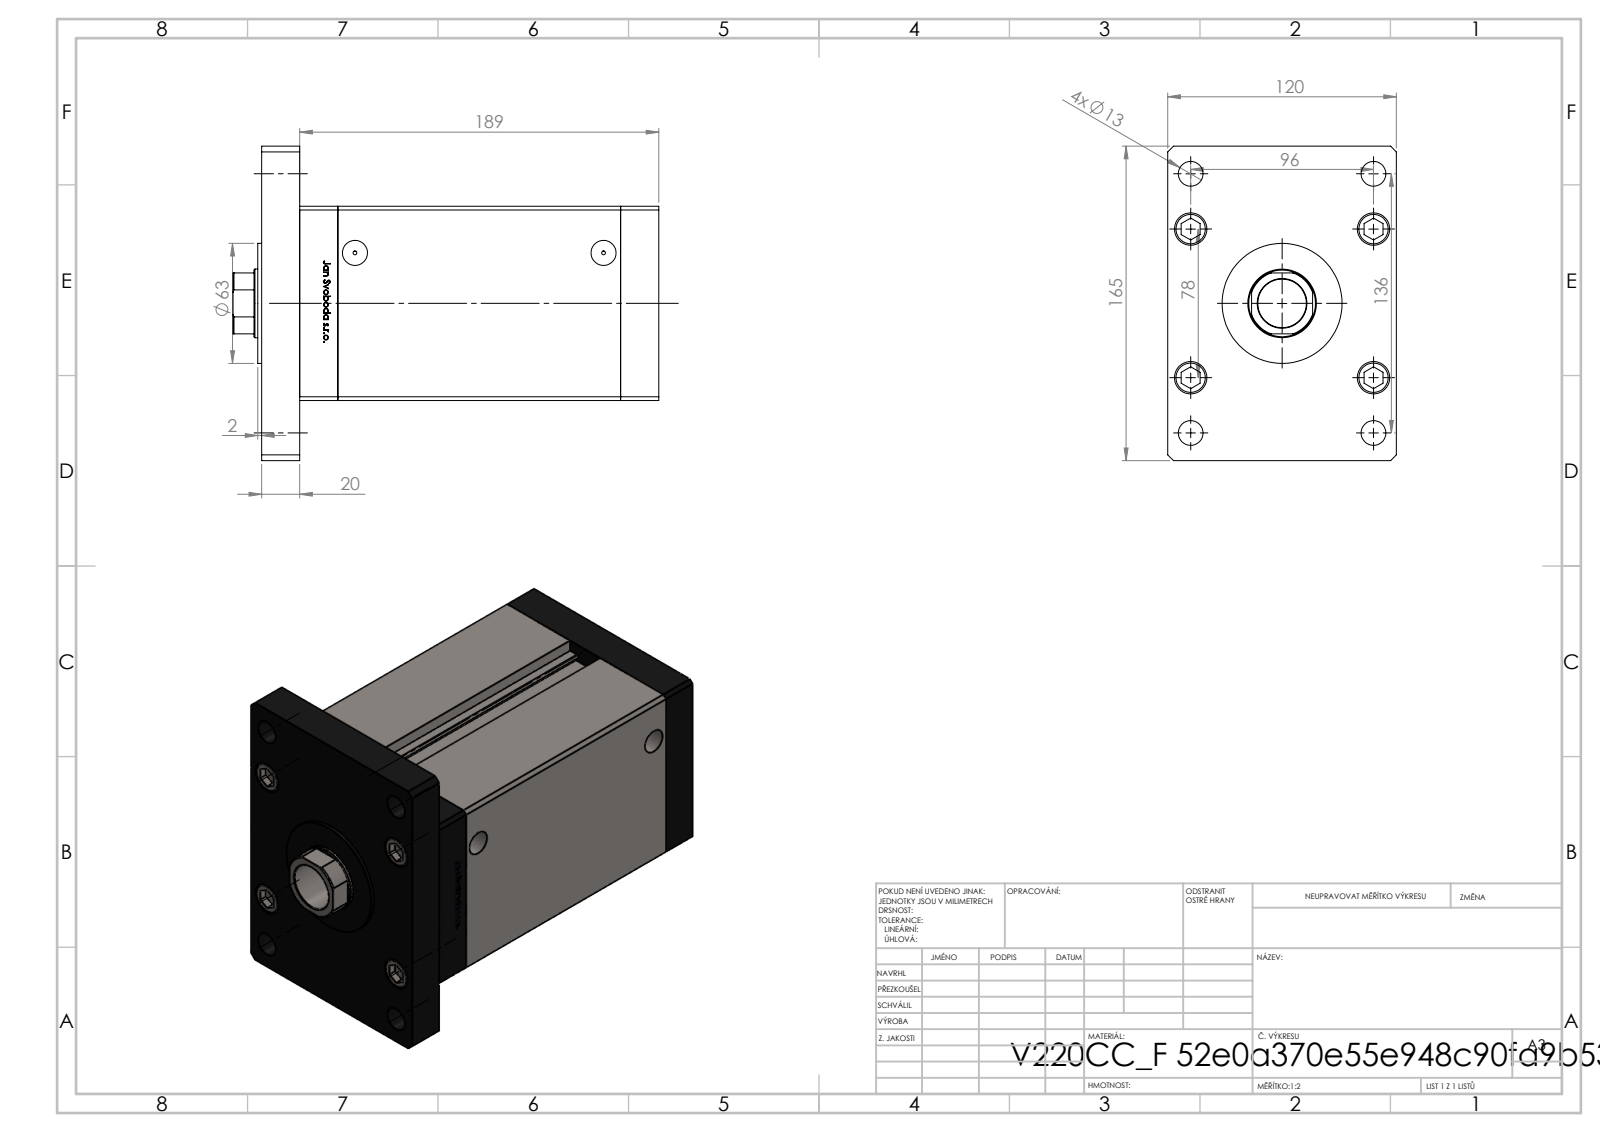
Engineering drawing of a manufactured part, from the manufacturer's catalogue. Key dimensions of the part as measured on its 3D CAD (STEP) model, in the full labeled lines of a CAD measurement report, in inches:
Part name (STEP PRODUCT): V220C_FRONT_F; V220C_F_MIDDLE; V220C_VC_F; V220C_F (+2 more)
STEP written by: SolidWorks 2019 (CONFIG_CONTROL_DESIGN)
Units: inches
Bodies: 19 solids, 1311 faces (517 planar, 188 cylindrical, 606 other)
Overall size (bounding box): 8.799 × 6.496 × 4.724
Volume: 147.5 in³ · Surface area: 498.2 in²
Round holes (diameter × count): ⌀0.531 ×5, ⌀0.709 ×5, ⌀0.472 ×4, ⌀0.512 ×4, ⌀0.669 ×4, ⌀0.079 ×2, ⌀0.518 ×2, ⌀1.004 ×1, ⌀1.417 ×1, ⌀1.476 ×1
Round bosses / shafts (diameter × count): ⌀0.315 ×9, ⌀0.669 ×5, ⌀2.48 ×1
Partial cylindrical surfaces — rounded edges, fillets, slot ends (radius × count): R0.037 ×2, R0.689 ×1
Main face-to-face distances: 0.787, 6.634, 7.421, 4.724, 4.016, 5.846, 1.575, 8.209, 1.348, 1.654
Hole centre spacings: 1.634, 1.142, 2.435, 3.277, 3.78, 3.948, 4.213, 5.659
